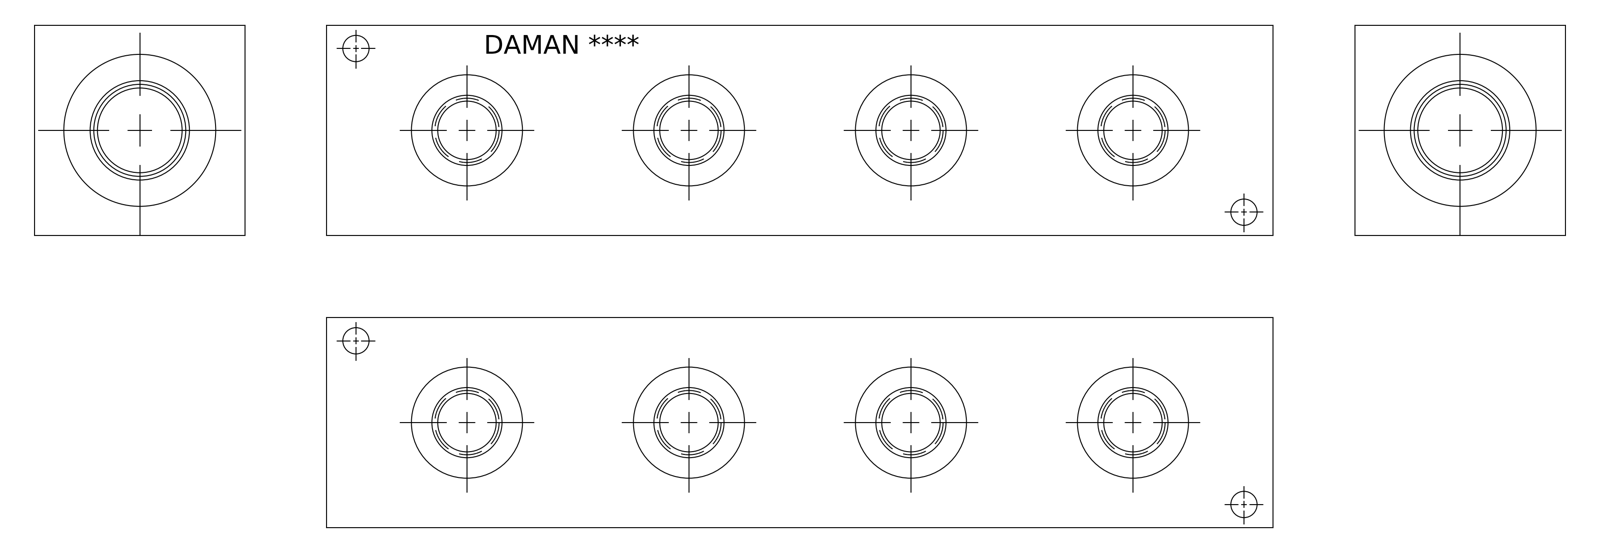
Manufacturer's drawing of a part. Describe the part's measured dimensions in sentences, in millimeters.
The part is named "Part_AH0900408S_3D". Its 3-D file was written by "Autodesk Inventor 2019 (AUTOMOTIVE_DESIGN)". It is 1 solid with 427 faces: 231 planar, 52 cylindrical and 144 other. Overall it measures 257.18 by 57.15 by 57.15 millimeters. Its volume is 746 905 cubic millimeters and its surface area 84 202 square millimeters. Round holes: 8 of diameter 17.5, 8 of diameter 19.05, 8 of diameter 19.25, 8 of diameter 30.63, 4 of diameter 7.14, 2 of diameter 15.88, 1 of diameter 23.01, 1 of diameter 24.92, 1 of diameter 26.99, 1 of diameter 27, 1 of diameter 27.43, 1 of diameter 42.04. The main face-to-face distances are 57.15, 0.79, 56.36, 257.18, 256.39, 255.6, 42.09, 14.27, 15.06, 19.84. The hole center spacings are 60.32, 120.65, 37.45, 37.48, 60.33, 93.16, 93.19, 152.43.
